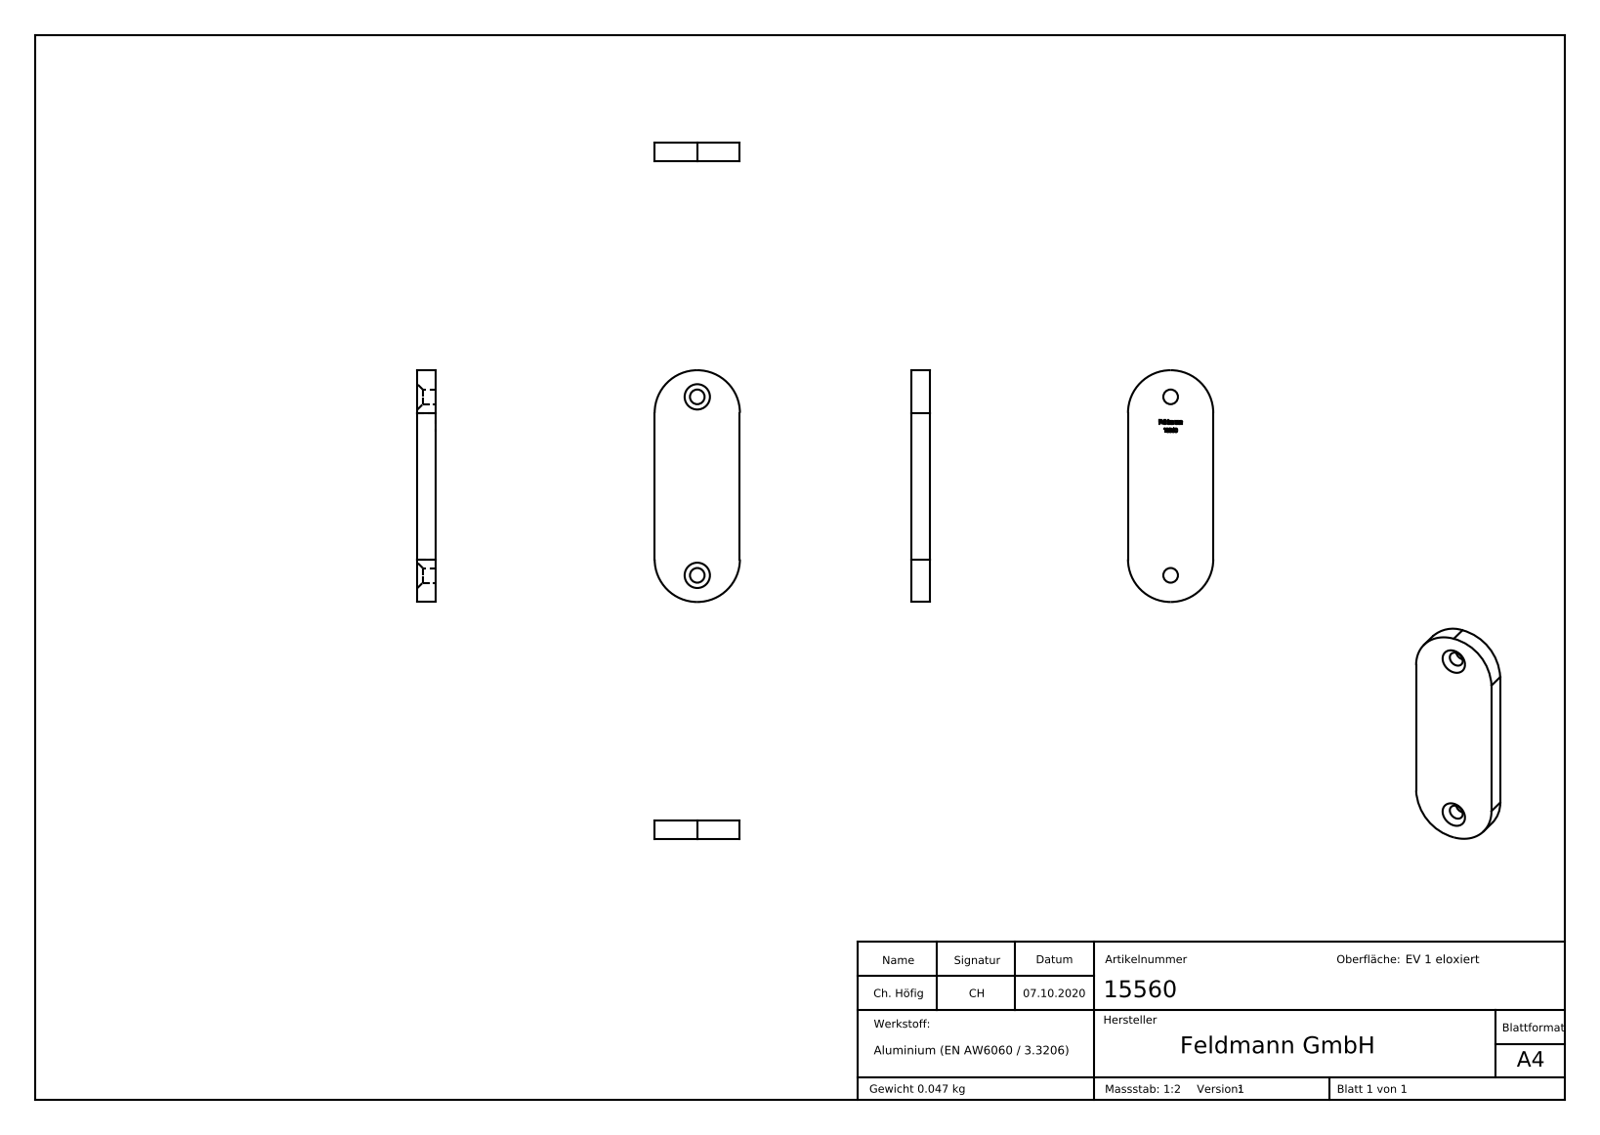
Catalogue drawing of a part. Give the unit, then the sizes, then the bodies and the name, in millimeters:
Units: millimetres
Overall size (bounding box): 87 × 32 × 7
Round holes (diameter × count): ⌀5.5 ×2
Partial cylindrical surfaces — rounded edges, fillets, slot ends (radius × count): R16 ×2
Main face-to-face distances: 7, 32, 6.9, 0.39, 2.97, 2.02, 1.12, 2.19, 1.08, 4.09
Hole centre spacings: 67
Volume: 17 531 mm³ · Surface area: 6 726 mm²
Bodies: 1 solid, 191 faces (97 planar, 8 cylindrical, 86 other)
Part name (STEP PRODUCT): AMF Schliessblech Konfig Teil1_15560; AMF Schliessblech Konfig Teil1; 15560
STEP written by: SolidWorks 2018 (CONFIG_CONTROL_DESIGN)
